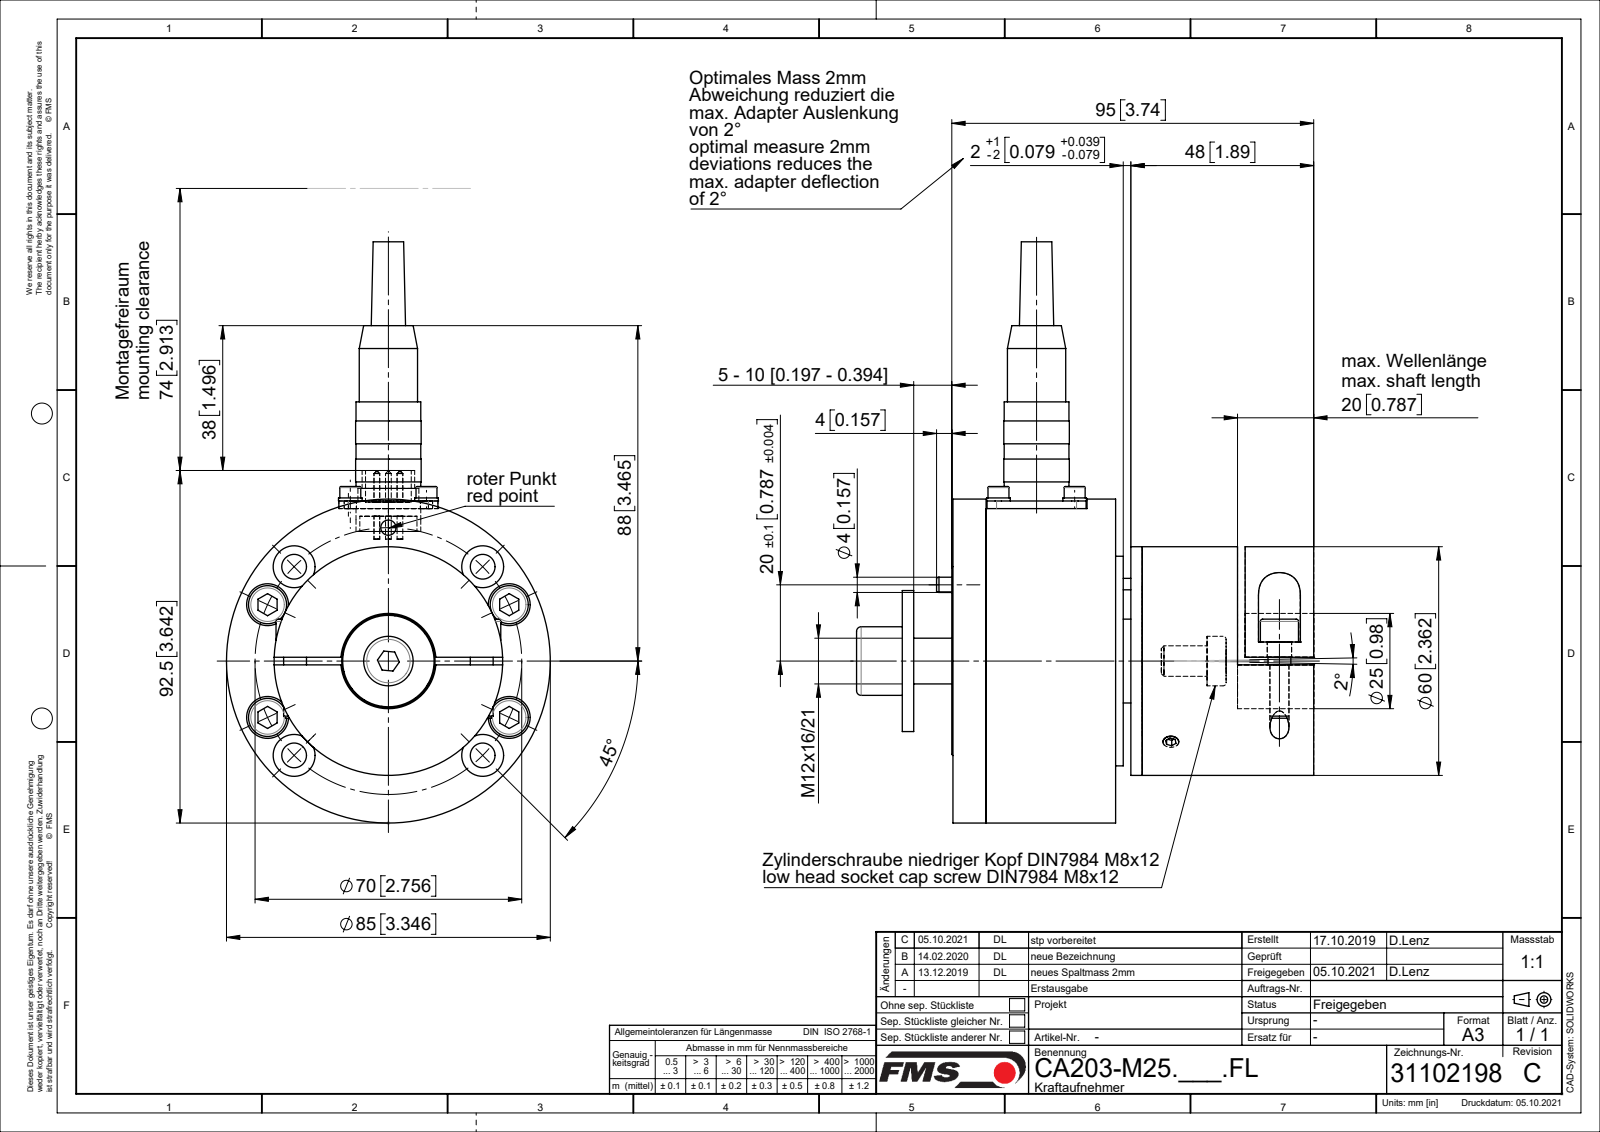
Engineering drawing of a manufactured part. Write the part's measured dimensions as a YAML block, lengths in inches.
part_name: "Spannstift_ISO13337_D04x10; Flanschstecker_M14x1_Mini_5pol; Zyl-Schr DIN912_M12x25; Sch DIN9021_M8 (+8 more)"
step_written_by: "SolidWorks 2018 (CONFIG_CONTROL_DESIGN)"
units: inches
bodies: {solids: 43, faces: 785, planar: 270, cylindrical: 326, other: 189}
overall_size: [6.004, 4.724, 3.346]
volume: 19.07
surface_area: 173.2
round_holes:
  - {diameter: 0.098, count: 8}
  - {diameter: 0.256, count: 8}
  - {diameter: 0.433, count: 8}
  - {diameter: 0.197, count: 6}
  - {diameter: 0.157, count: 5}
  - {diameter: 0.122, count: 4}
  - {diameter: 0.126, count: 4}
  - {diameter: 0.142, count: 4}
  - {diameter: 0.276, count: 4}
  - {diameter: 0.118, count: 2}
  - {diameter: 0.252, count: 2}
  - {diameter: 0.165, count: 1}
round_bosses_or_shafts:
  - {diameter: 0.118, count: 8}
  - {diameter: 0.236, count: 7}
  - {diameter: 0.394, count: 6}
  - {diameter: 0.059, count: 5}
  - {diameter: 0.244, count: 4}
  - {diameter: 0.224, count: 4}
  - {diameter: 0.217, count: 4}
  - {diameter: 3.346, count: 1}
partial_cylinders:
  - {radius: 0.098, count: 4}
  - {radius: 0.197, count: 2}
  - {radius: 0.217, count: 2}
face_to_face_distances: [0.079, 1.614, 1.772, 0.394, 1.181, 0.118, 1.969, 0.866, 2.362, 1.339]
hole_center_spacings: [1.378, 0.787, 0.976, 0.992, 1.291, 2.013, 2.223, 1.113]
